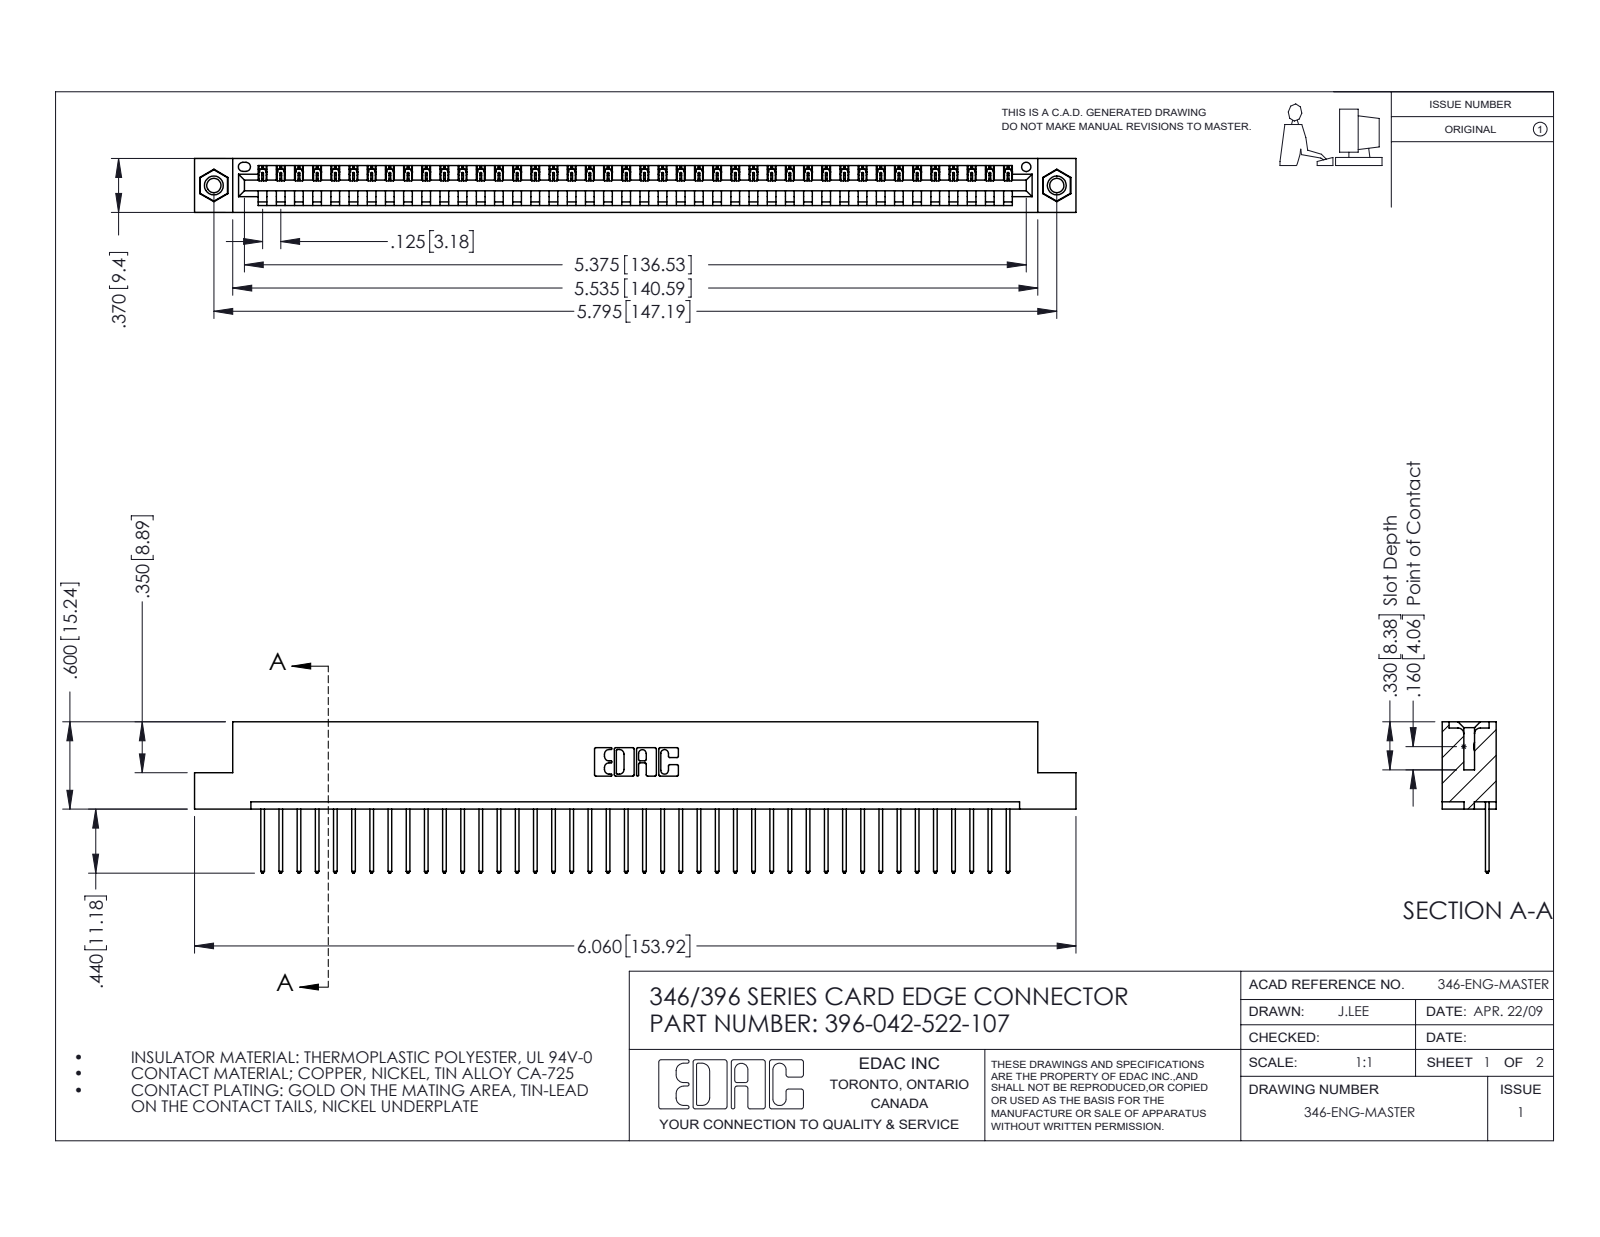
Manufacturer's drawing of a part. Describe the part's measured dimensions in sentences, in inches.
The part is named "345-292-001_345-293-122; 346 Part_Flush Mounting Lugs - 0.156 Dia-TI; 345-250-001_345-250-005-103; 396-042-522-107". Its 3-D file was written by "SolidWorks 2016 (CONFIG_CONTROL_DESIGN)". It is 45 solids with 2618 faces: 1788 planar, 814 cylindrical and 16 other. Overall it measures 6.06 by 1.04 by 0.37 inches. Its volume is 0.899 cubic inches and its surface area 28.82 square inches. Round holes: 2 of diameter 0.098, 2 of diameter 0.125, 2 of diameter 0.156, 1 of diameter 0.064. Round bosses or shafts: 2 of diameter 0.155. Partial cylindrical surfaces (rounded edges, fillets, slot ends): 84 of radius 0.006, 84 of radius 0.01, 22 of radius 0.01, 6 of radius 0.007, 6 of radius 0.031, 3 of radius 0.026, 2 of radius 0.031, 2 of radius 0.04. The main face-to-face distances are 0.048, 0.322, 0.37, 0.25, 0.072, 0.298, 0.025, 0.148, 0.222, 0.1. The hole center spacings are 0.246, 5.586, 5.795.
